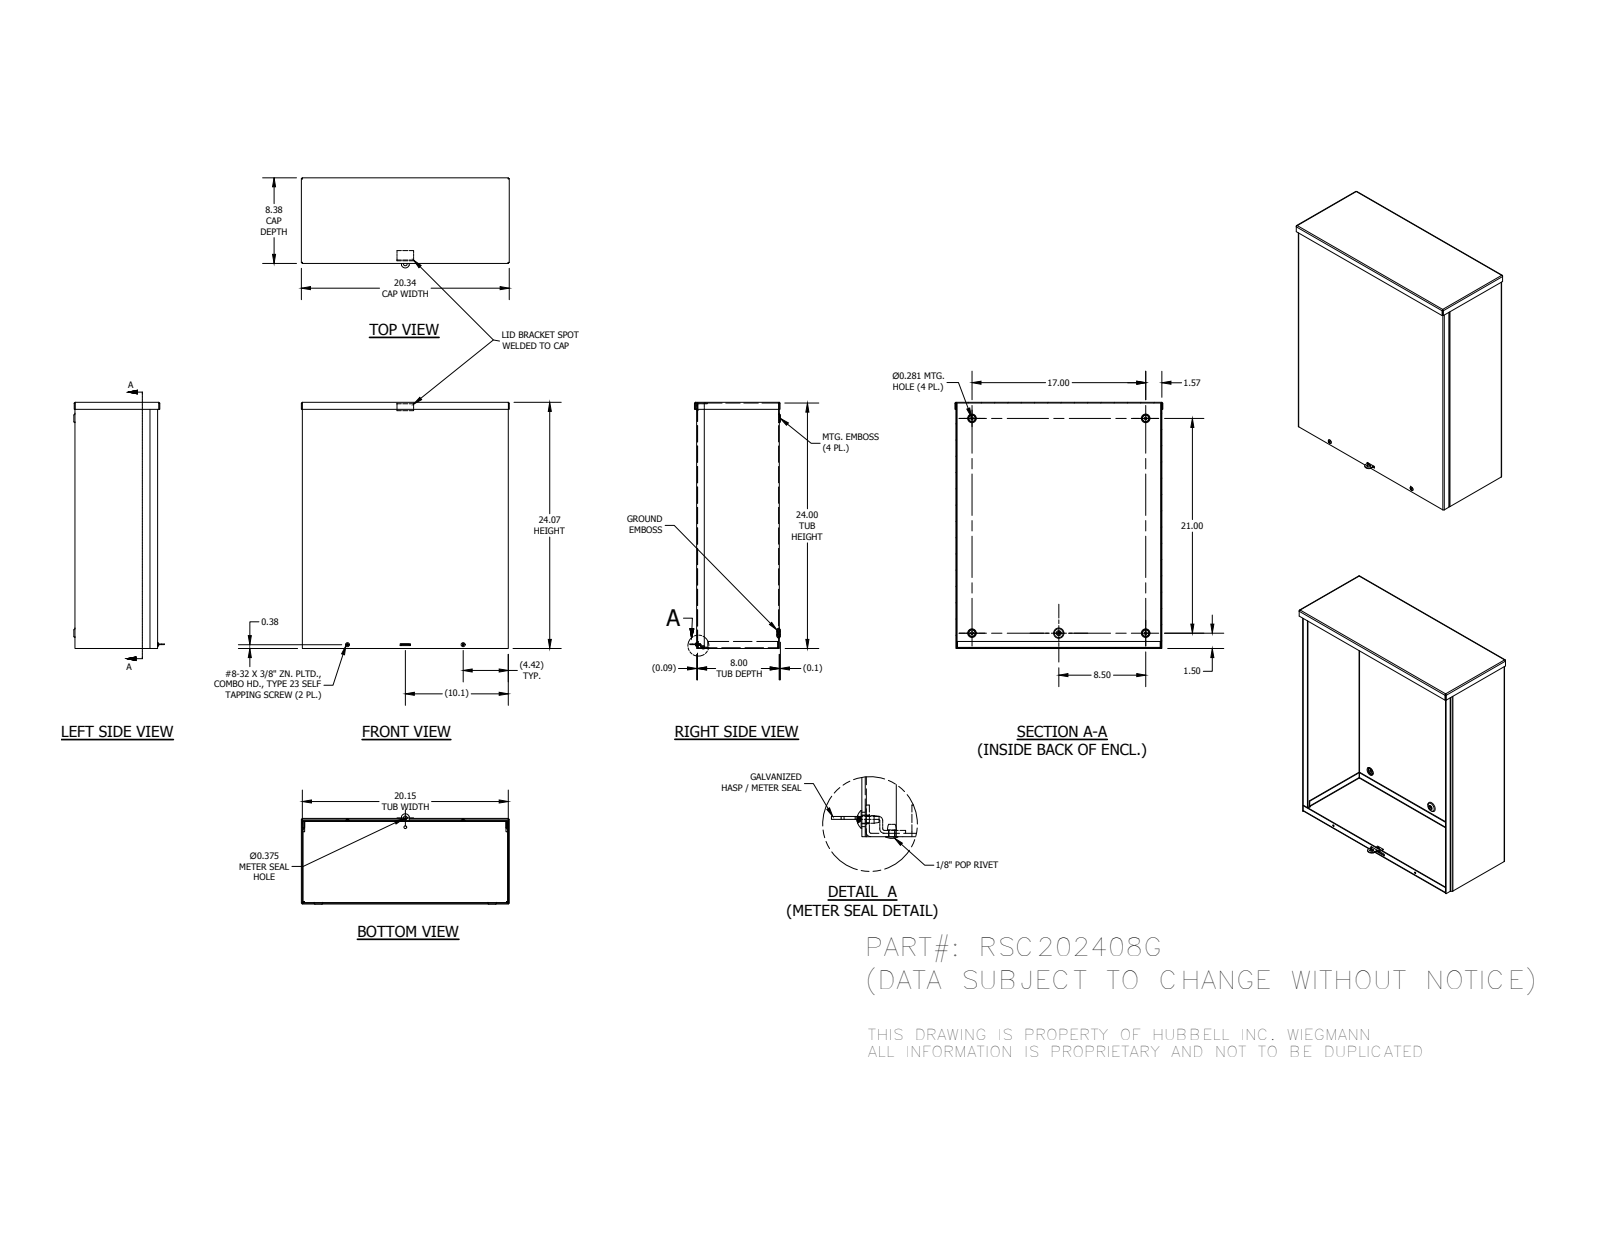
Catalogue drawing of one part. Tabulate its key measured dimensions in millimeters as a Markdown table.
| quantity | value |
| --- | --- |
| part name | RSC202408GBKPA; RSC2008GEWPA; RSC2024GLFA; RSC2008GCPA (+5 more) |
| STEP written by | Autodesk Inventor 2014 (AUTOMOTIVE_DESIGN) |
| units | millimeters |
| bodies | 9 solids, 320 faces (183 planar, 61 cylindrical, 76 other) |
| overall size | 612.5 × 516.52 × 224.8 |
| volume | 2 154 000 mm³ |
| surface area | 2 309 000 mm² |
| round holes (diameter × count) | 7.14 × 4, 7.94 × 4, 3.73 × 2, 3.17 × 1, 3.45 × 1, 4.34 × 1, 9.52 × 1 |
| round bosses / shafts (diameter × count) | 9.75 × 2, 4.17 × 2, 6.65 × 1, 5.93 × 1, 3.17 × 1 |
| partial cylindrical surfaces (radius × count) | 0.79 × 19, 2.67 × 17, 2.37 × 2, 10.16 × 1 |
| main face-to-face distances | 1.88, 203.6, 205.48, 201.72, 509.88, 609.6, 508, 511.76, 611.48, 607.72 |
| hole center spacings | 77.68, 360.7, 287.34, 566.6, 667.17, 146.48, 215.9, 431.8 |
